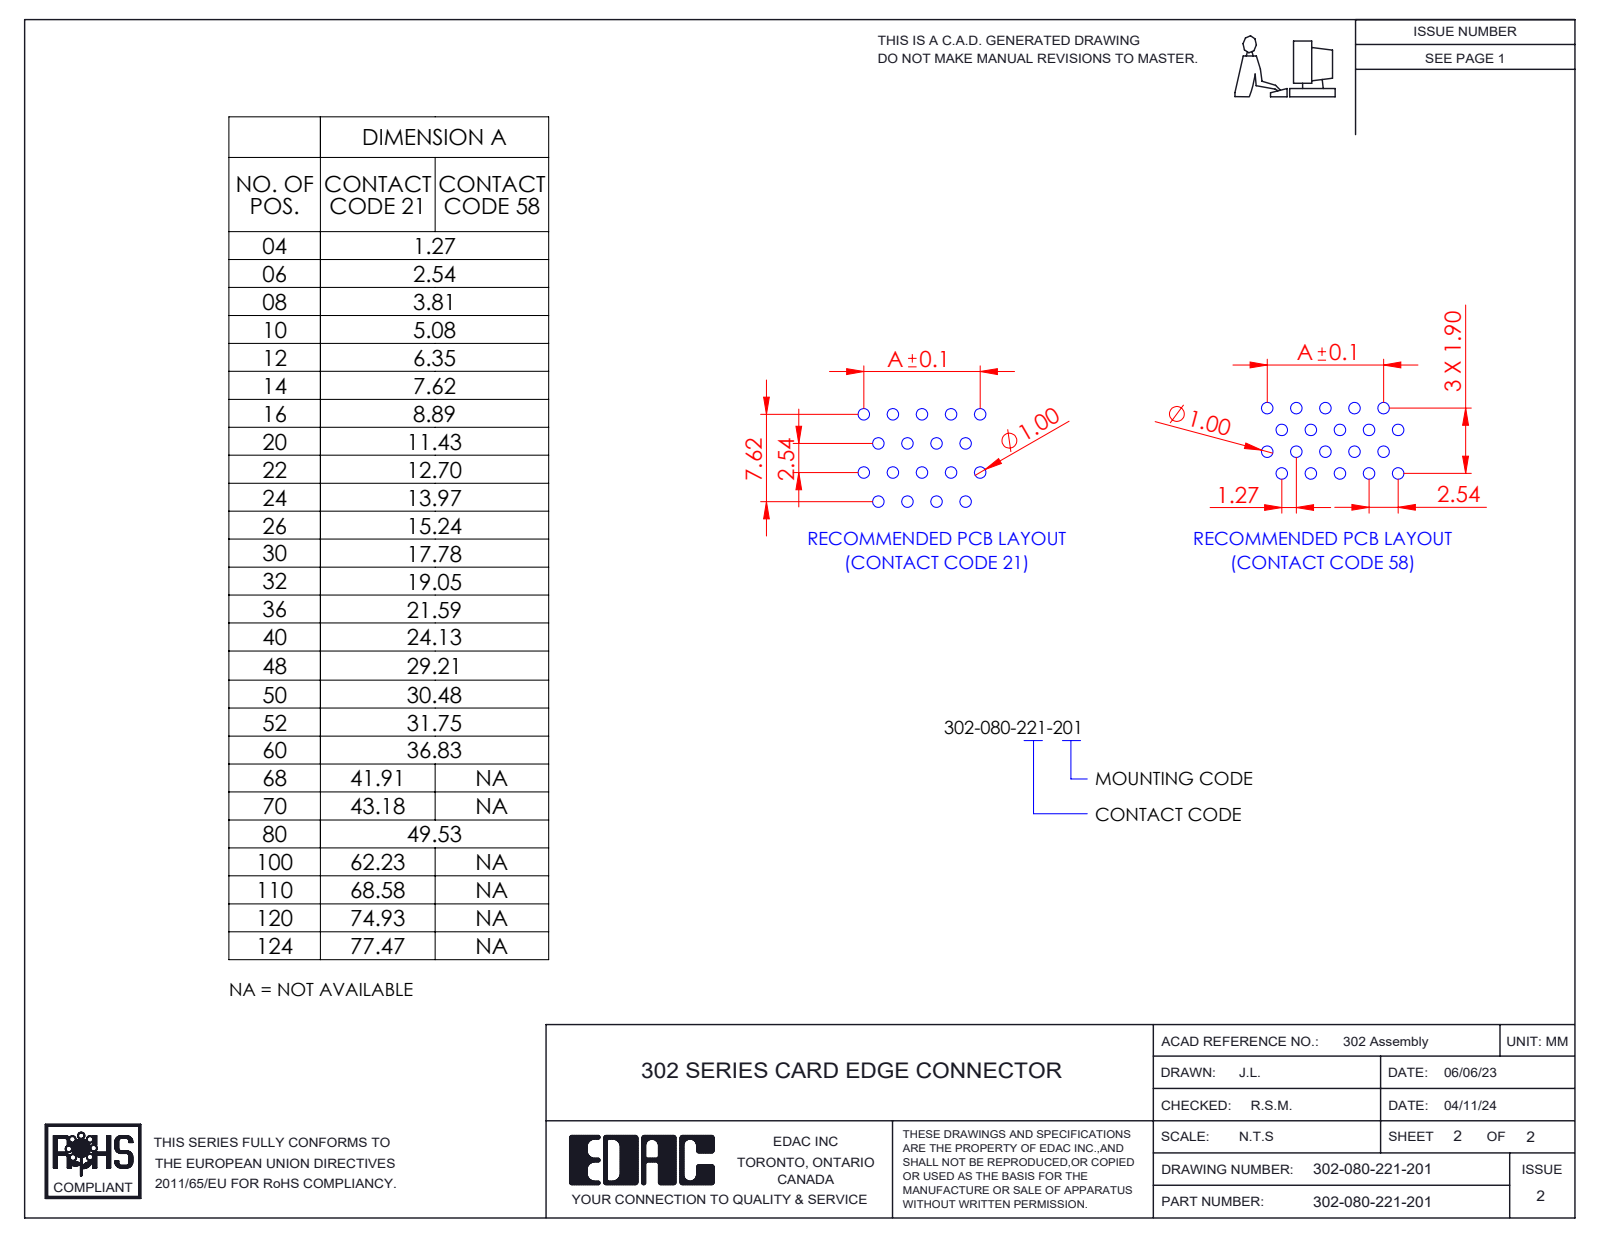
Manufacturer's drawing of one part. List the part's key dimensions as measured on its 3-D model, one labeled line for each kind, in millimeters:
Part name (STEP PRODUCT): Contact_302-290-X21 (1); 302-080-221-201; HSG_Vertical HSG; Contact_302-290-X21 (2)
STEP written by: SolidWorks 2023 (CONFIG_CONTROL_DESIGN)
Units: millimetres
Bodies: 81 solids, 3706 faces (2729 planar, 813 cylindrical, 164 other)
Overall size (bounding box): 56.9 × 17.63 × 8.88
Volume: 4 394 mm³ · Surface area: 12 188 mm²
Partial cylindrical surfaces — rounded edges, fillets, slot ends (radius × count): R0.2 ×88, R2.03 ×4, R2.09 ×4, R0.11 ×2, R0.4 ×2, R0.41 ×2, R1.25 ×2, R1.53 ×2
Main face-to-face distances: 2.54, 1.27, 5.08, 3.81, 7.62, 6.35, 8.88, 8.89, 10.16, 11.43
